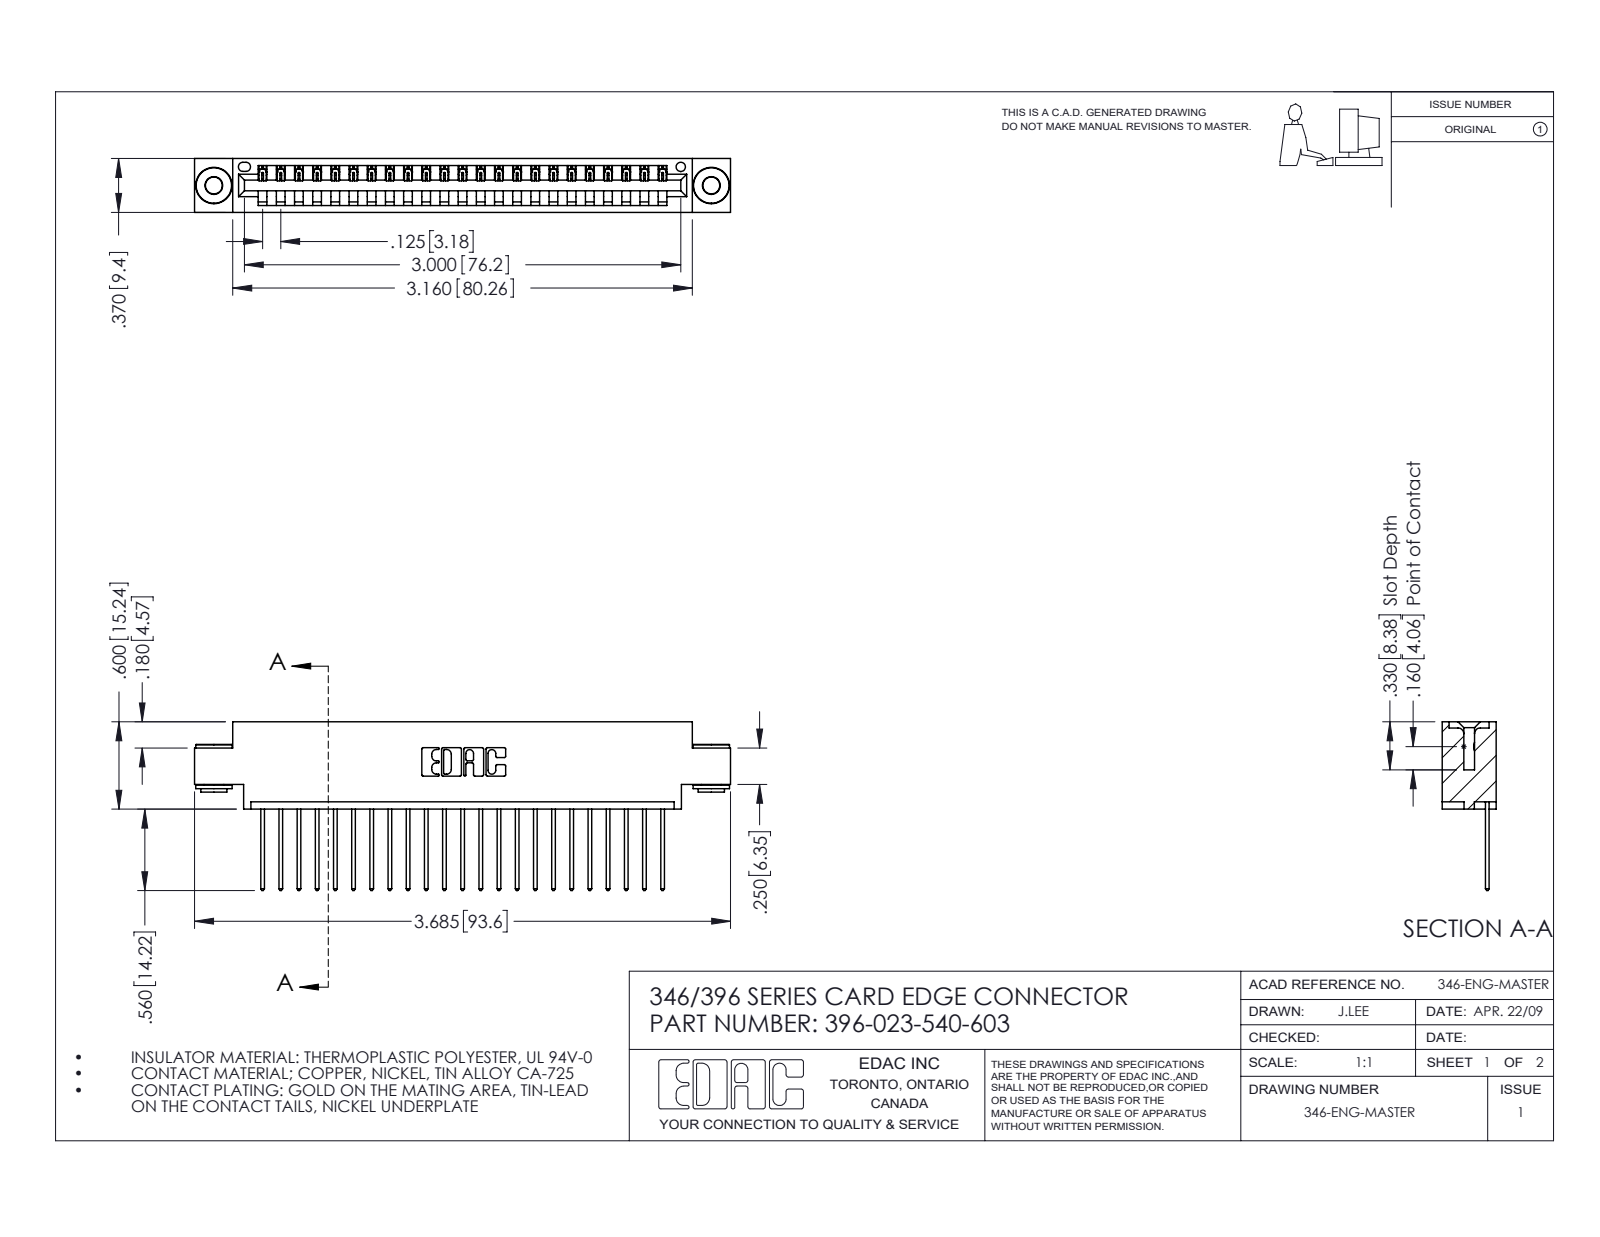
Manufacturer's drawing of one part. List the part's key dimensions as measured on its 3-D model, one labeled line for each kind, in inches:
Part name (STEP PRODUCT): 345-250-002_345-250-002-102; 346 Part_0.170 Offset - 0.156 Dia-TH; 345-292-001_345-293-140; 396-023-540-603
STEP written by: SolidWorks 2016 (CONFIG_CONTROL_DESIGN)
Units: inches
Bodies: 26 solids, 1498 faces (1010 planar, 480 cylindrical, 8 other)
Overall size (bounding box): 3.685 × 1.16 × 0.37
Volume: 0.532 in³ · Surface area: 17.52 in²
Round holes (diameter × count): ⌀0.116 ×2, ⌀0.156 ×2, ⌀0.064 ×1
Round bosses / shafts (diameter × count): ⌀0.25 ×2, ⌀0.18 ×2, ⌀0.136 ×2
Partial cylindrical surfaces — rounded edges, fillets, slot ends (radius × count): R0.006 ×46, R0.01 ×46, R0.01 ×22, R0.007 ×6, R0.031 ×6, R0.026 ×3, R0.031 ×2, R0.04 ×2
Main face-to-face distances: 0.048, 0.322, 0.37, 0.25, 0.025, 0.072, 0.298, 0.148, 0.222, 0.1
Hole centre spacings: 0.246, 3.212, 3.42
